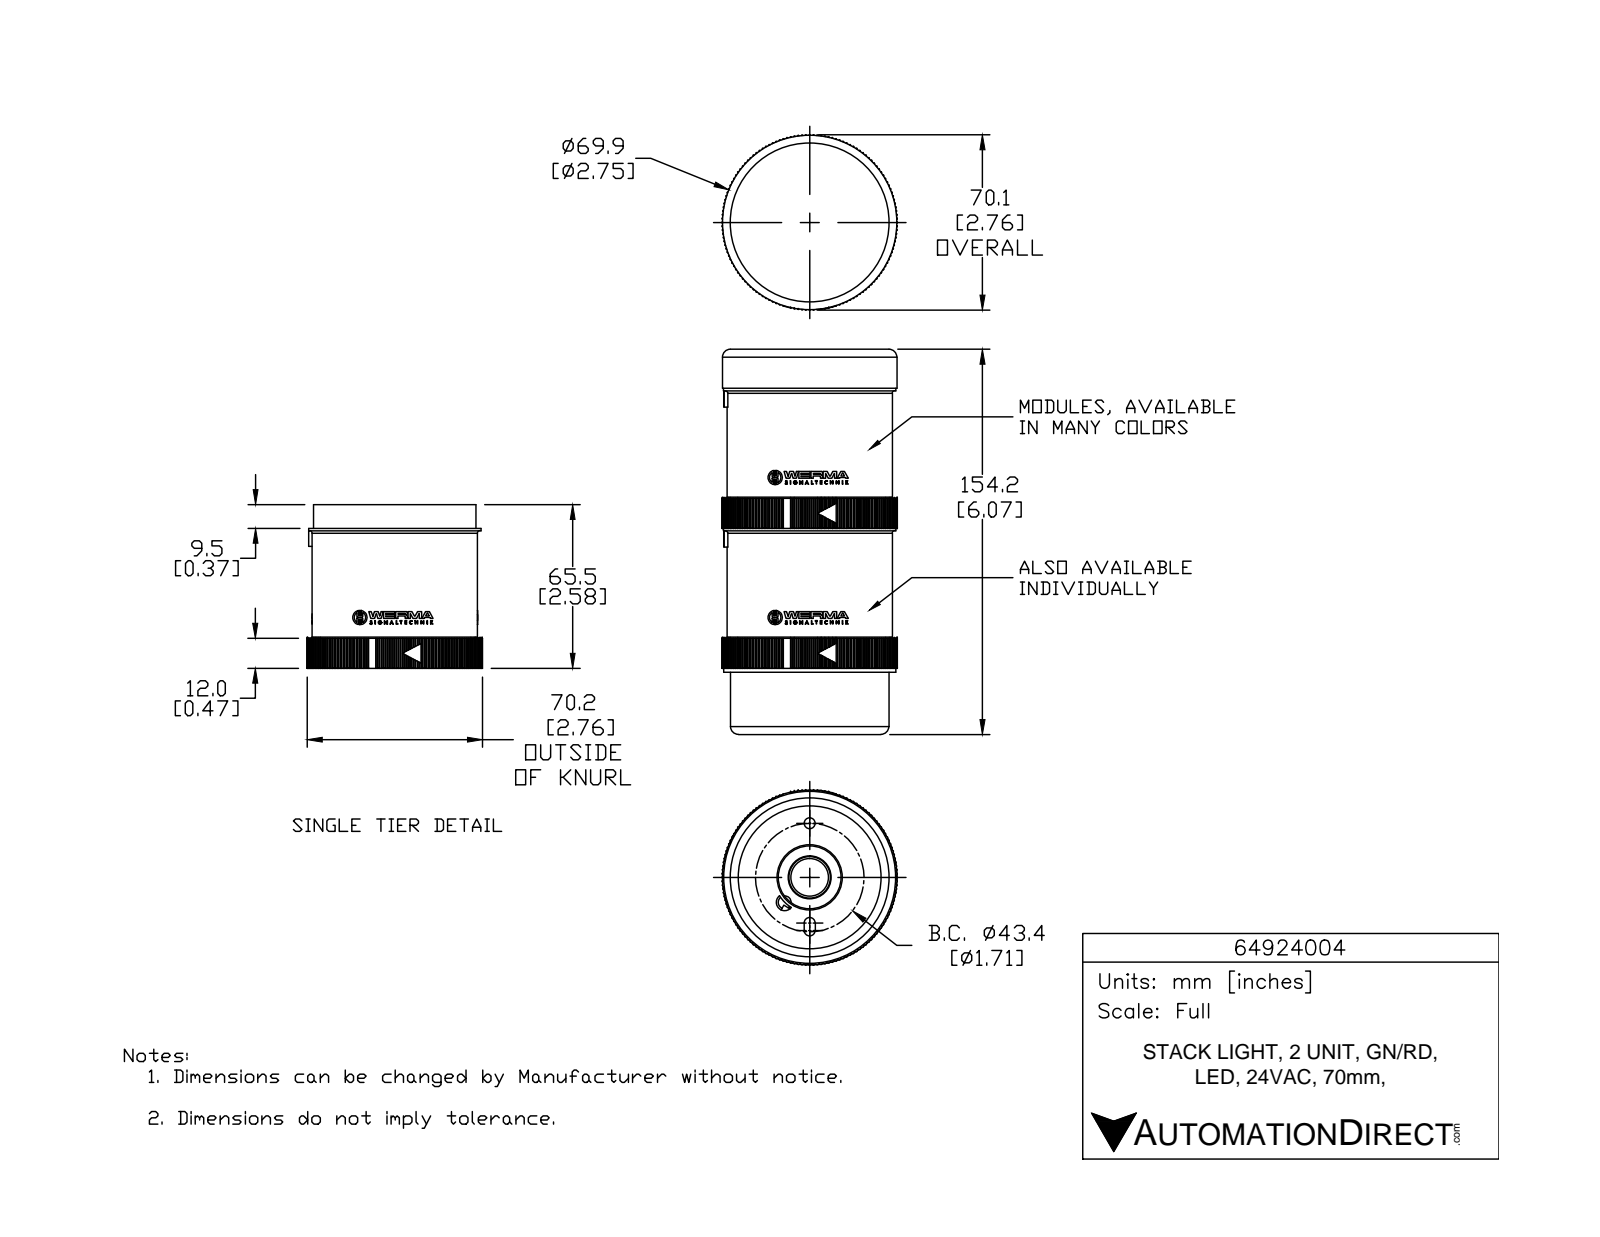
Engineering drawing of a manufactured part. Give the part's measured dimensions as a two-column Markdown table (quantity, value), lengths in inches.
| quantity | value |
| --- | --- |
| part name | 64924002_CAP; 649_3D Modell; 64924002_ORING; 64924002_BASE (+2 more) |
| STEP written by | SolidWorks 2014 (AUTOMOTIVE_DESIGN) |
| units | inches |
| bodies | 7 solids, 2860 faces (1613 planar, 1187 cylindrical, 60 other) |
| overall size | 6.07 × 2.762 × 2.762 |
| volume | 7.139 in³ |
| surface area | 228.7 in² |
| round holes (diameter × count) | 0.18 × 6, 0.175 × 1, 0.2 × 1, 0.255 × 1, 0.347 × 1, 0.595 × 1, 0.991 × 1, 1.857 × 1, 2.339 × 1, 2.392 × 1, 2.539 × 1, 2.65 × 1 |
| round bosses / shafts (diameter × count) | 2.75 × 1, 2.717 × 1, 2.712 × 1, 2.559 × 1, 2.552 × 1, 2.499 × 1, 1.151 × 1, 0.675 × 1 |
| partial cylindrical surfaces (radius × count) | 0.008 × 285, 0.03 × 12, 0.059 × 12, 0.085 × 6, 0.105 × 6, 0.087 × 2, 0.127 × 2, 0.168 × 2 |
| main face-to-face distances | 2.205, 0.076, 1.767, 0.025, 0.05, 0.343, 2.498, 2.548, 0.293, 1.769 |
| hole center spacings | 0.761, 0.761, 1.319, 1.522, 0.271, 0.421, 0.435, 0.533 |
